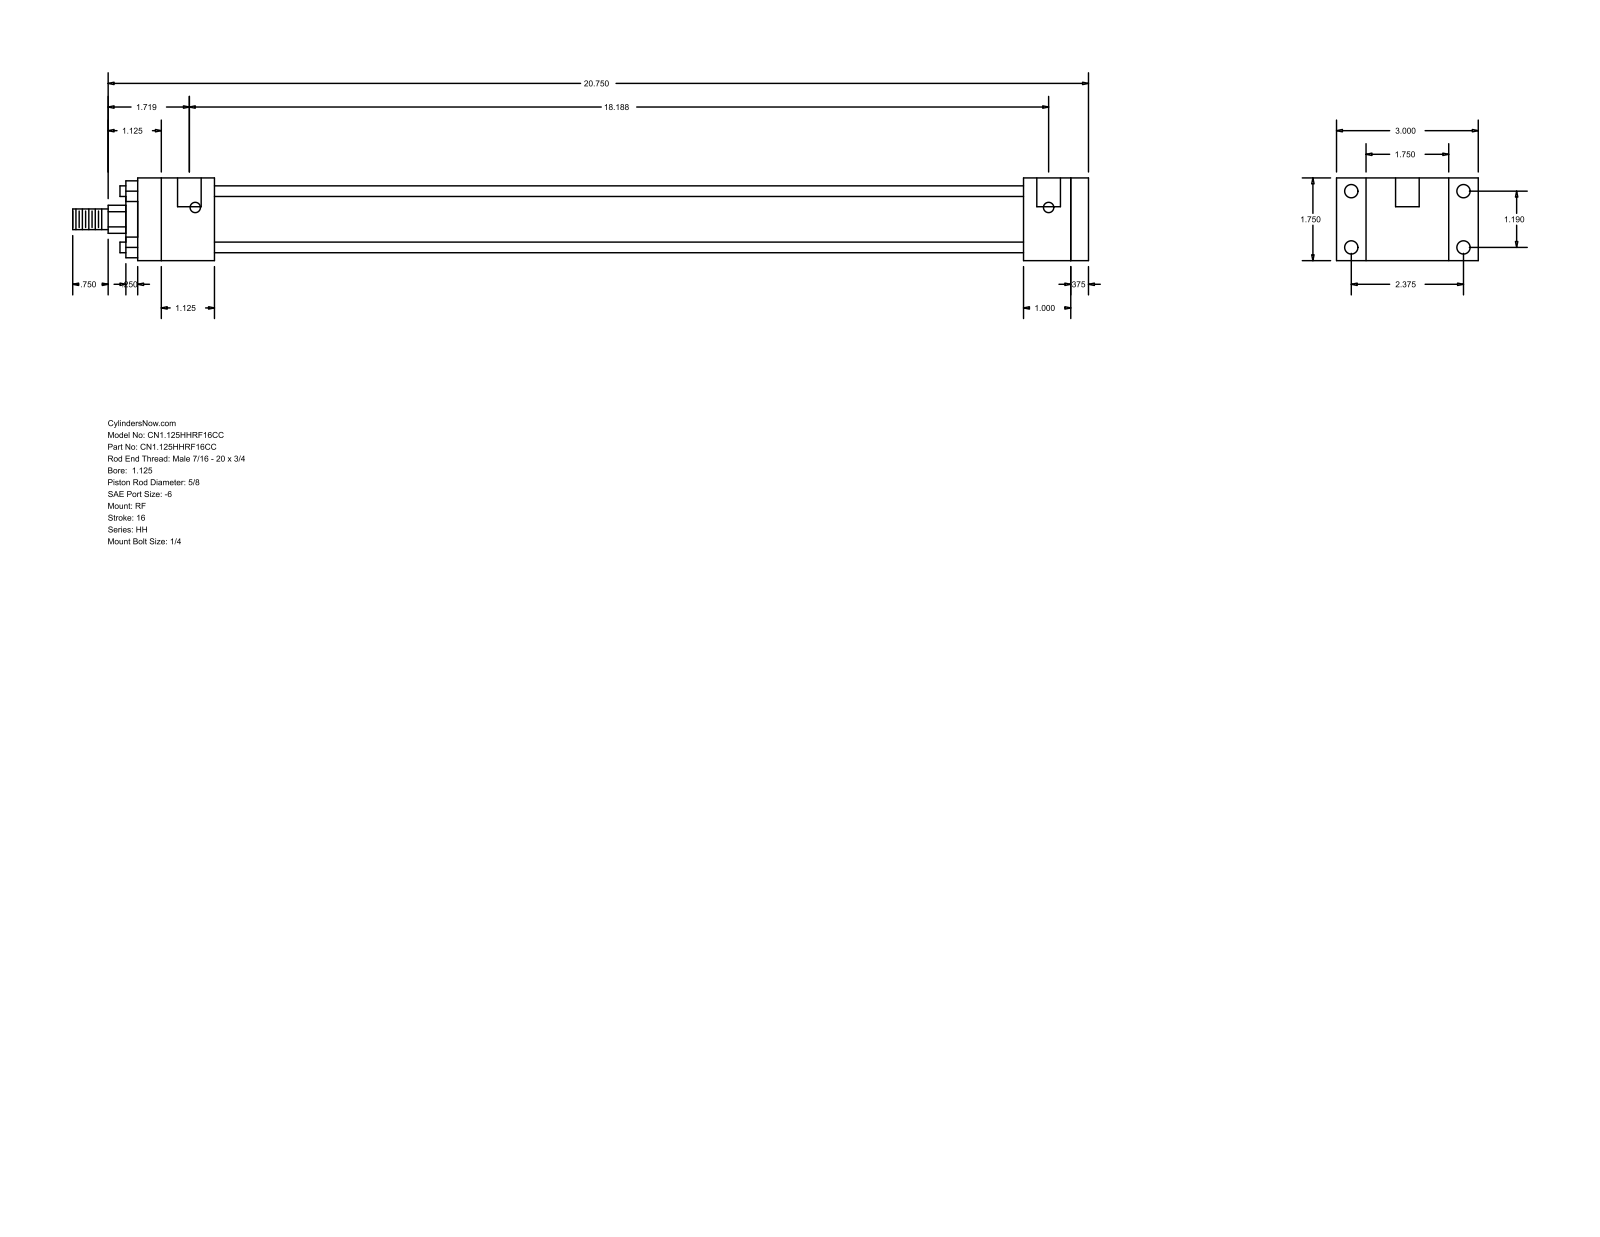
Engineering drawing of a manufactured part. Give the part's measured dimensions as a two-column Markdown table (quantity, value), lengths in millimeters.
| quantity | value |
| --- | --- |
| part name | HH_RF__0112_0.625 |
| STEP written by | GSSL Pune (CONFIG_CONTROL_DESIGN) |
| units | millimeters |
| bodies | 0 solids, 92 faces (64 planar, 28 cylindrical, 0 other) |
| overall size | 546.1 × 76.2 × 44.45 |
| round holes (diameter × count) | 5.56 × 4, 7.14 × 4, 12.7 × 2 |
| round bosses / shafts (diameter × count) | 5.71 × 4, 34.92 × 1, 28.57 × 1, 15.88 × 1, 11.11 × 1 |
| partial cylindrical surfaces (radius × count) | 7.54 × 1 |
| main face-to-face distances | 44.46, 9.53, 511.17, 25.4, 34.93, 15.87, 460.37, 469.9, 434.97, 41.27 |
| hole center spacings | 30.22, 60.32, 67.47, 458.79, 3.17, 461.96 |
